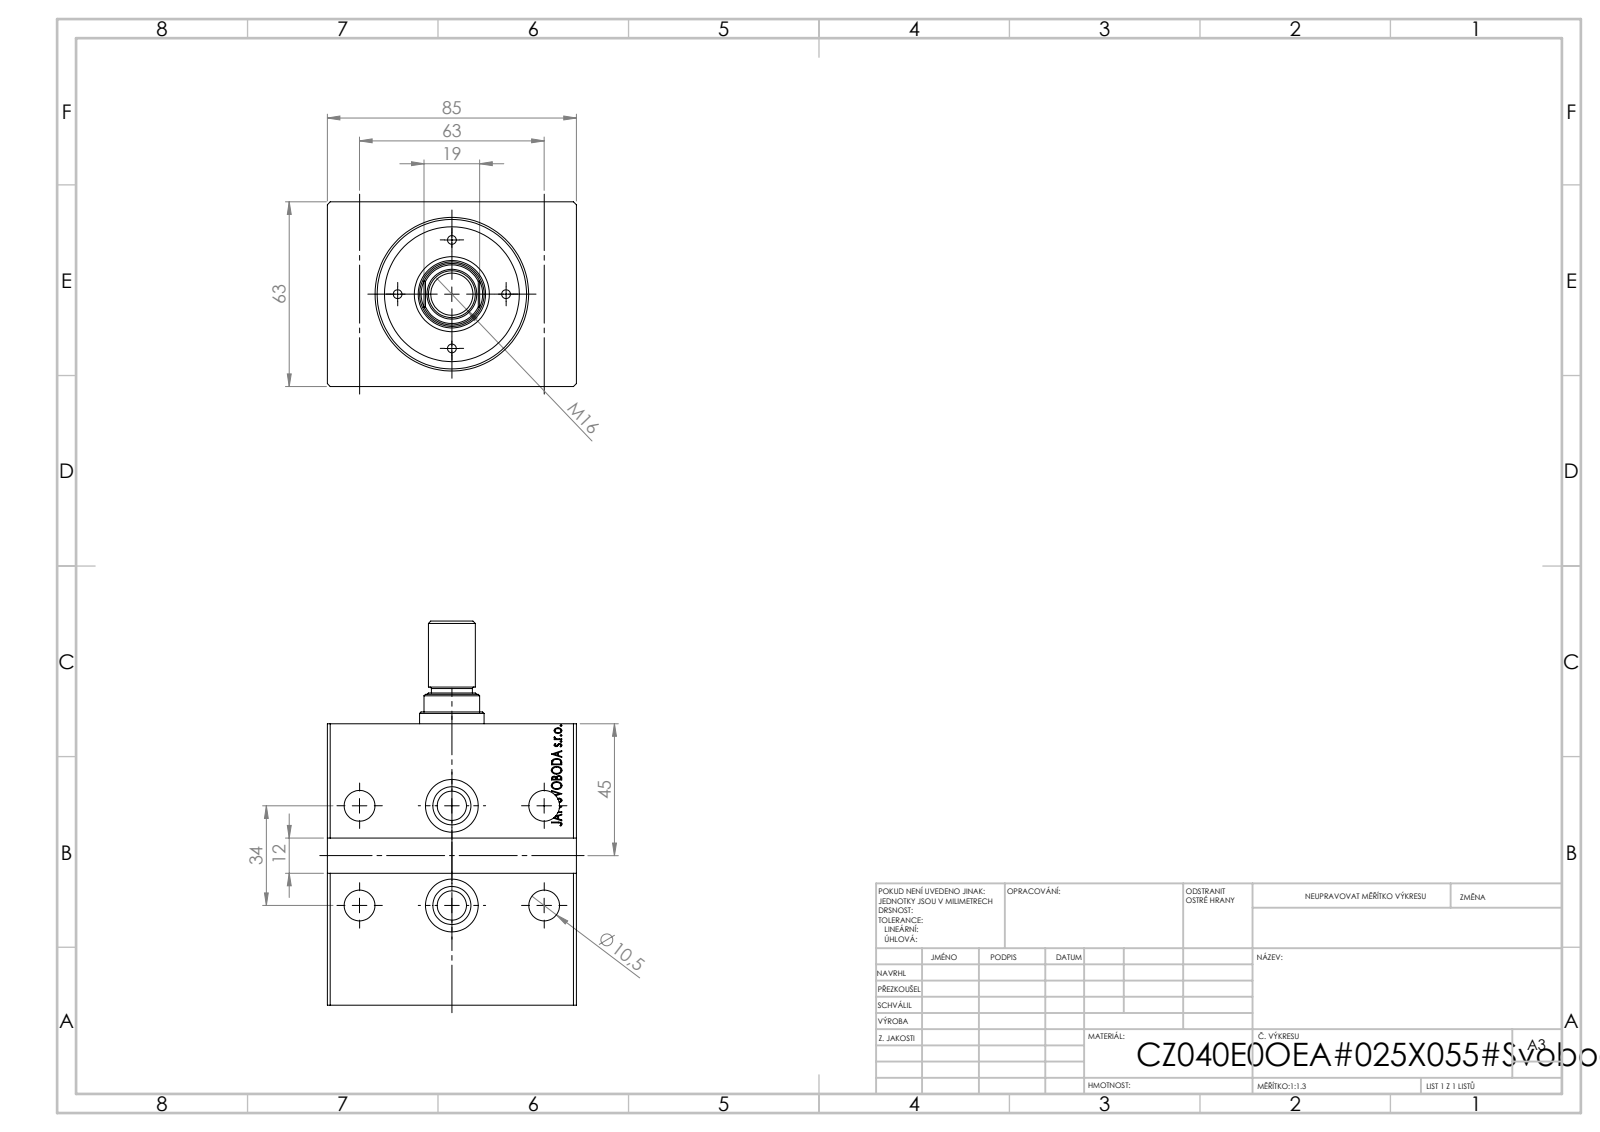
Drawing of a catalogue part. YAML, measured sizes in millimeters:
step_written_by: "SolidWorks 2019 (CONFIG_CONTROL_DESIGN)"
units: millimeters
bodies: {solids: 1, faces: 779, planar: 383, cylindrical: 30, other: 366}
overall_size: [96, 85, 63]
volume: 379357
surface_area: 58001
round_holes:
  - {diameter: 10.5, count: 4}
  - {diameter: 8, count: 2}
  - {diameter: 10, count: 2}
  - {diameter: 18, count: 2}
  - {diameter: 36, count: 1}
  - {diameter: 40, count: 1}
  - {diameter: 51, count: 1}
round_bosses_or_shafts:
  - {diameter: 13, count: 2}
face_to_face_distances: [63, 85, 96, 80.7, 15.3, 2, 61, 95.8, 15.1, 10]
hole_center_spacings: [31.5, 46.35, 34, 63, 71.59, 15.65, 16.92, 18.85]
